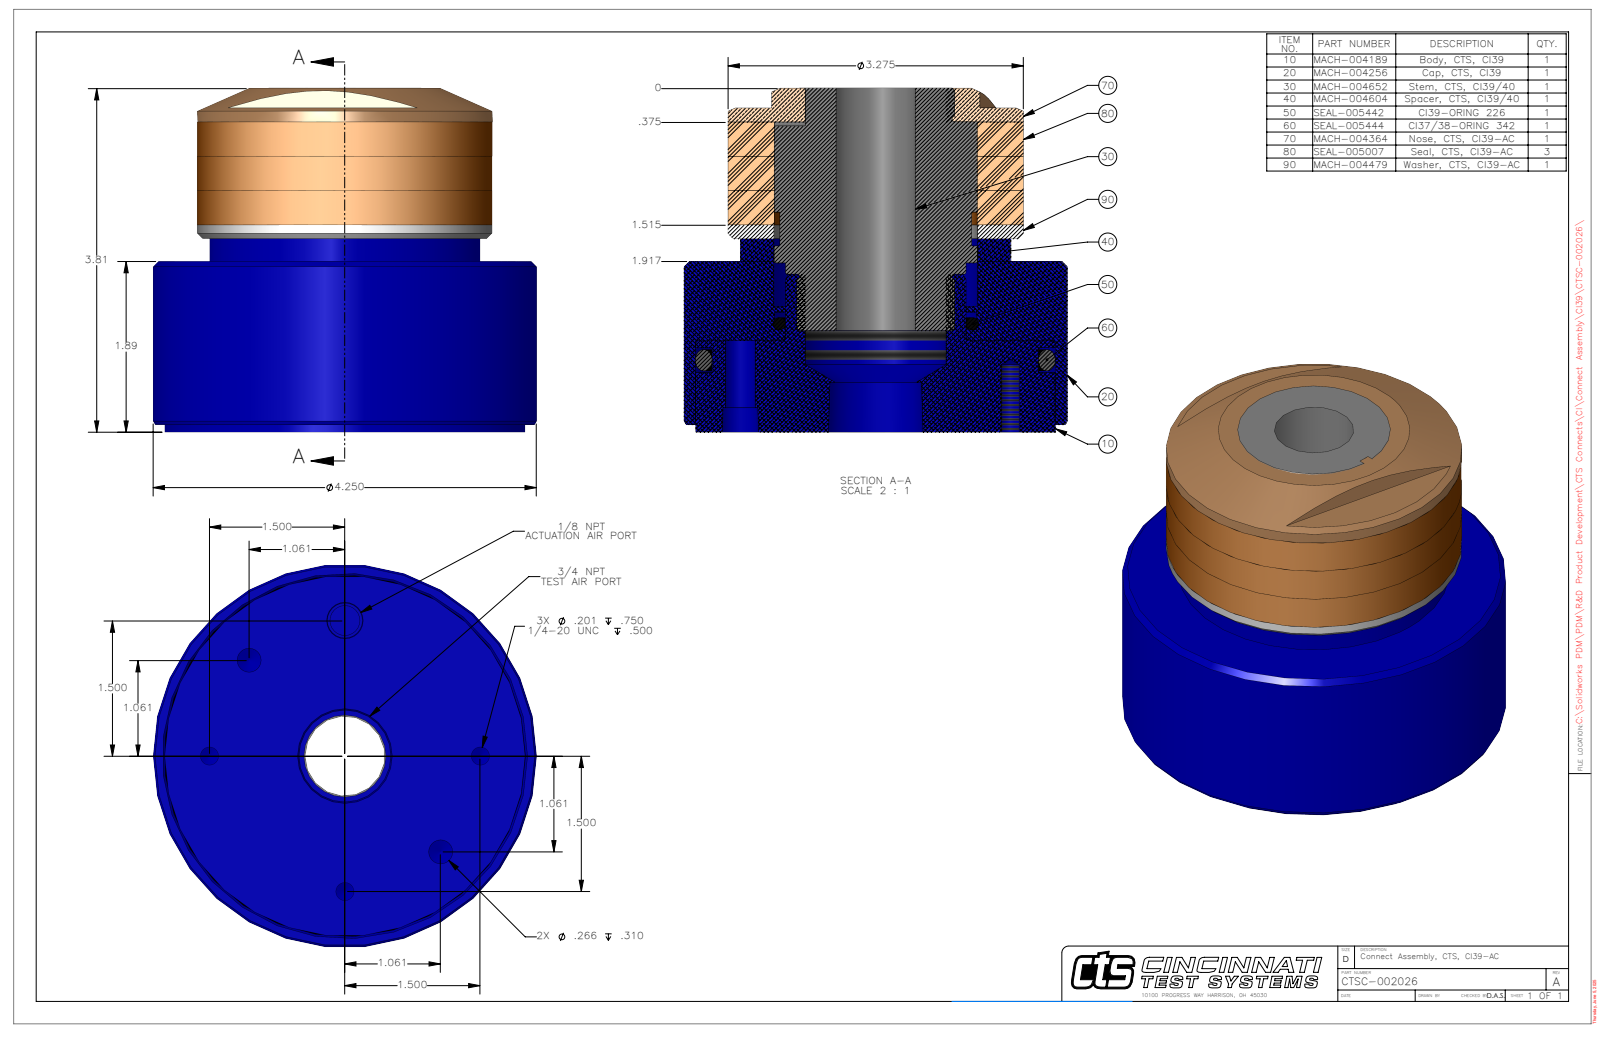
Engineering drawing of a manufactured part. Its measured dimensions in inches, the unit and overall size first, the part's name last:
Units: inches
Overall size (bounding box): 4.25 × 4.25 × 3.813
Round holes (diameter × count): ⌀0.201 ×3, ⌀0.266 ×2, ⌀0.332 ×1, ⌀0.88 ×1, ⌀2.25 ×1, ⌀2.26 ×1, ⌀2.261 ×1, ⌀4 ×1
Round bosses / shafts (diameter × count): ⌀4.25 ×1, ⌀3.992 ×1, ⌀3.275 ×1, ⌀3 ×1, ⌀2.12 ×1
Partial cylindrical surfaces — rounded edges, fillets, slot ends (radius × count): R0.062 ×1, R0.781 ×1
Main face-to-face distances: 1.893, 3.813, 1.92, 3.81, 1.917, 3.591, 1.698, 0.219, 0.222, 0.083
Hole centre spacings: 1.5, 1.148, 2.121, 2.772, 3
Volume: 39.05 in³ · Surface area: 104 in²
Bodies: 1 solid, 94 faces (32 planar, 39 cylindrical, 23 other)
Part name (STEP PRODUCT): CTSC-002026
STEP written by: SolidWorks 2023 (AUTOMOTIVE_DESIGN)
